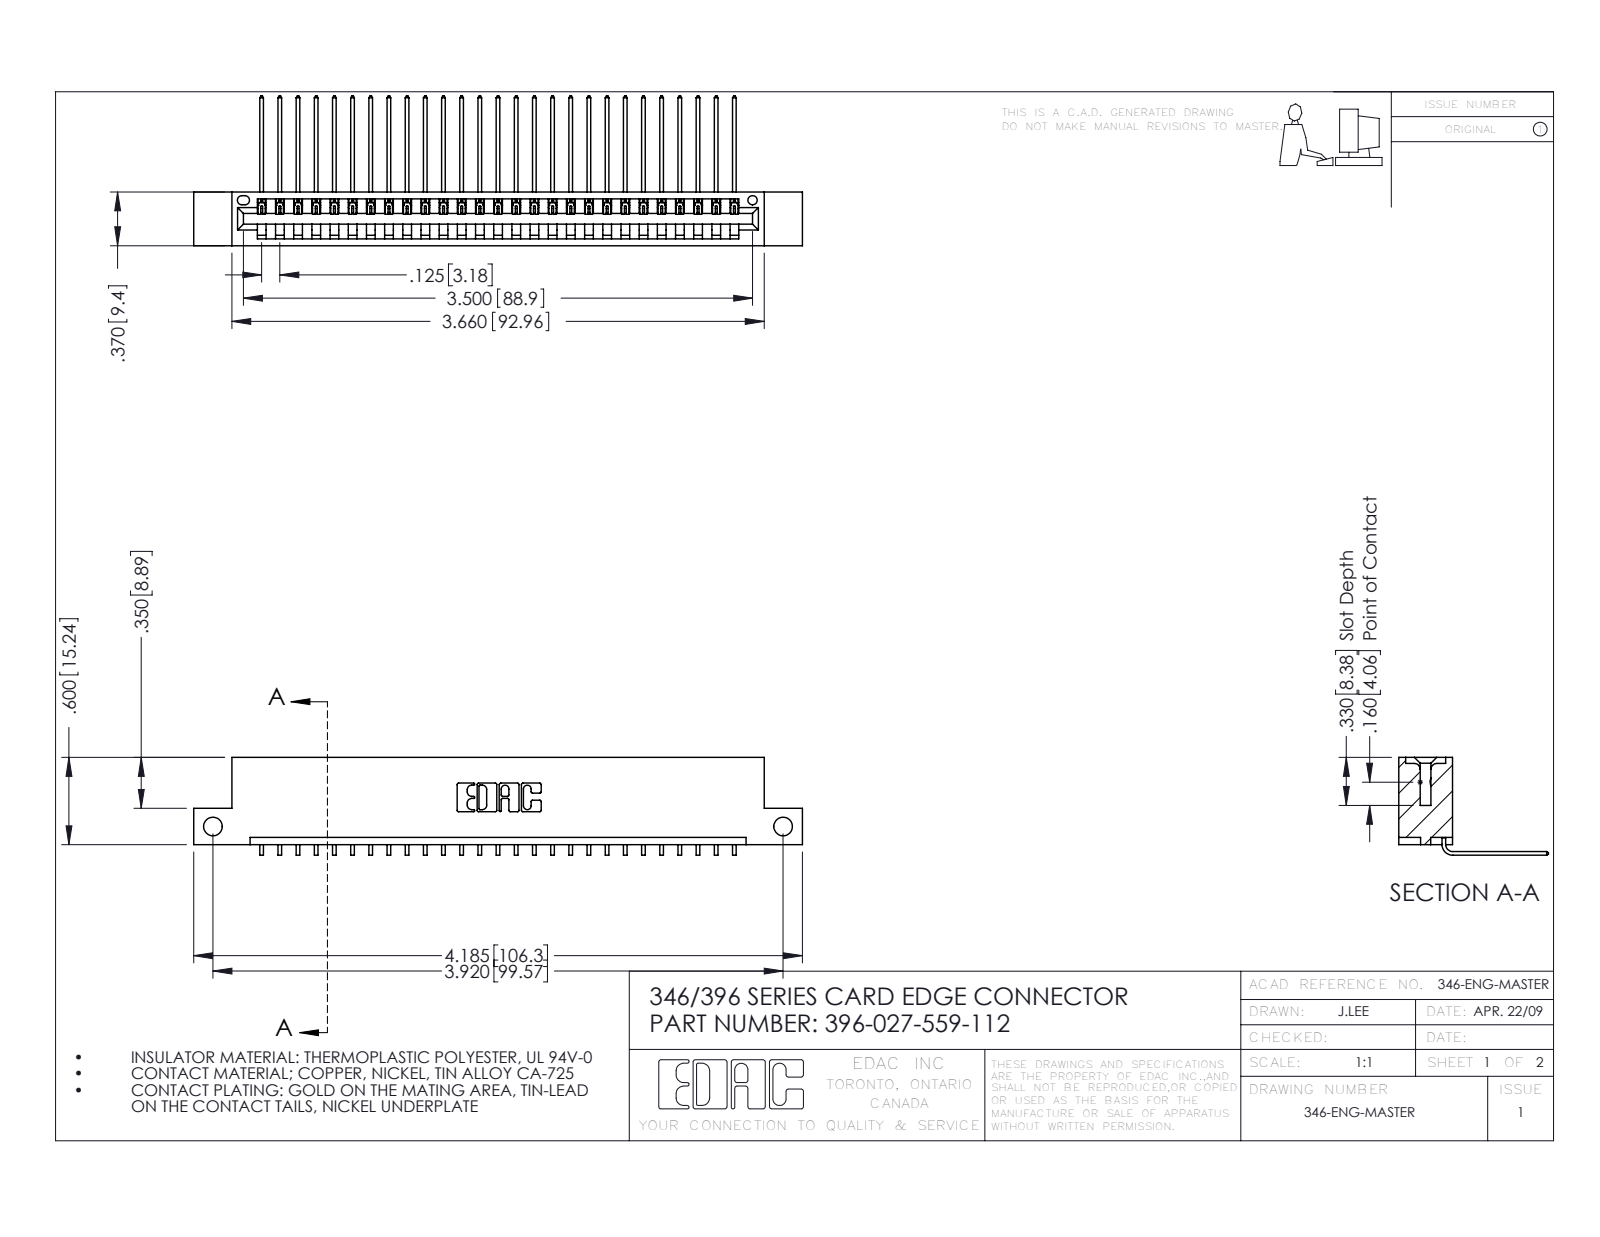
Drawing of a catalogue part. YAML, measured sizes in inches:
part_name: "346 Part_Flush Mounting Lugs - Side Mount; 345-292-001_558 559 Tail - 1; 396-027-559-112"
step_written_by: "SolidWorks 2016 (CONFIG_CONTROL_DESIGN)"
units: inches
bodies: {solids: 28, faces: 1742, planar: 1210, cylindrical: 532, other: 0}
overall_size: [4.185, 1.03, 0.673]
volume: 0.615
surface_area: 19.87
round_holes:
  - {diameter: 0.128, count: 2}
  - {diameter: 0.064, count: 1}
partial_cylinders:
  - {radius: 0.006, count: 54}
  - {radius: 0.01, count: 22}
  - {radius: 0.007, count: 6}
  - {radius: 0.031, count: 6}
  - {radius: 0.026, count: 3}
  - {radius: 0.031, count: 2}
  - {radius: 0.04, count: 2}
  - {radius: 0.014, count: 1}
face_to_face_distances: [0.048, 0.322, 0.37, 0.25, 0.072, 0.025, 0.298, 0.148, 0.222, 0.1]
hole_center_spacings: [3.92]
